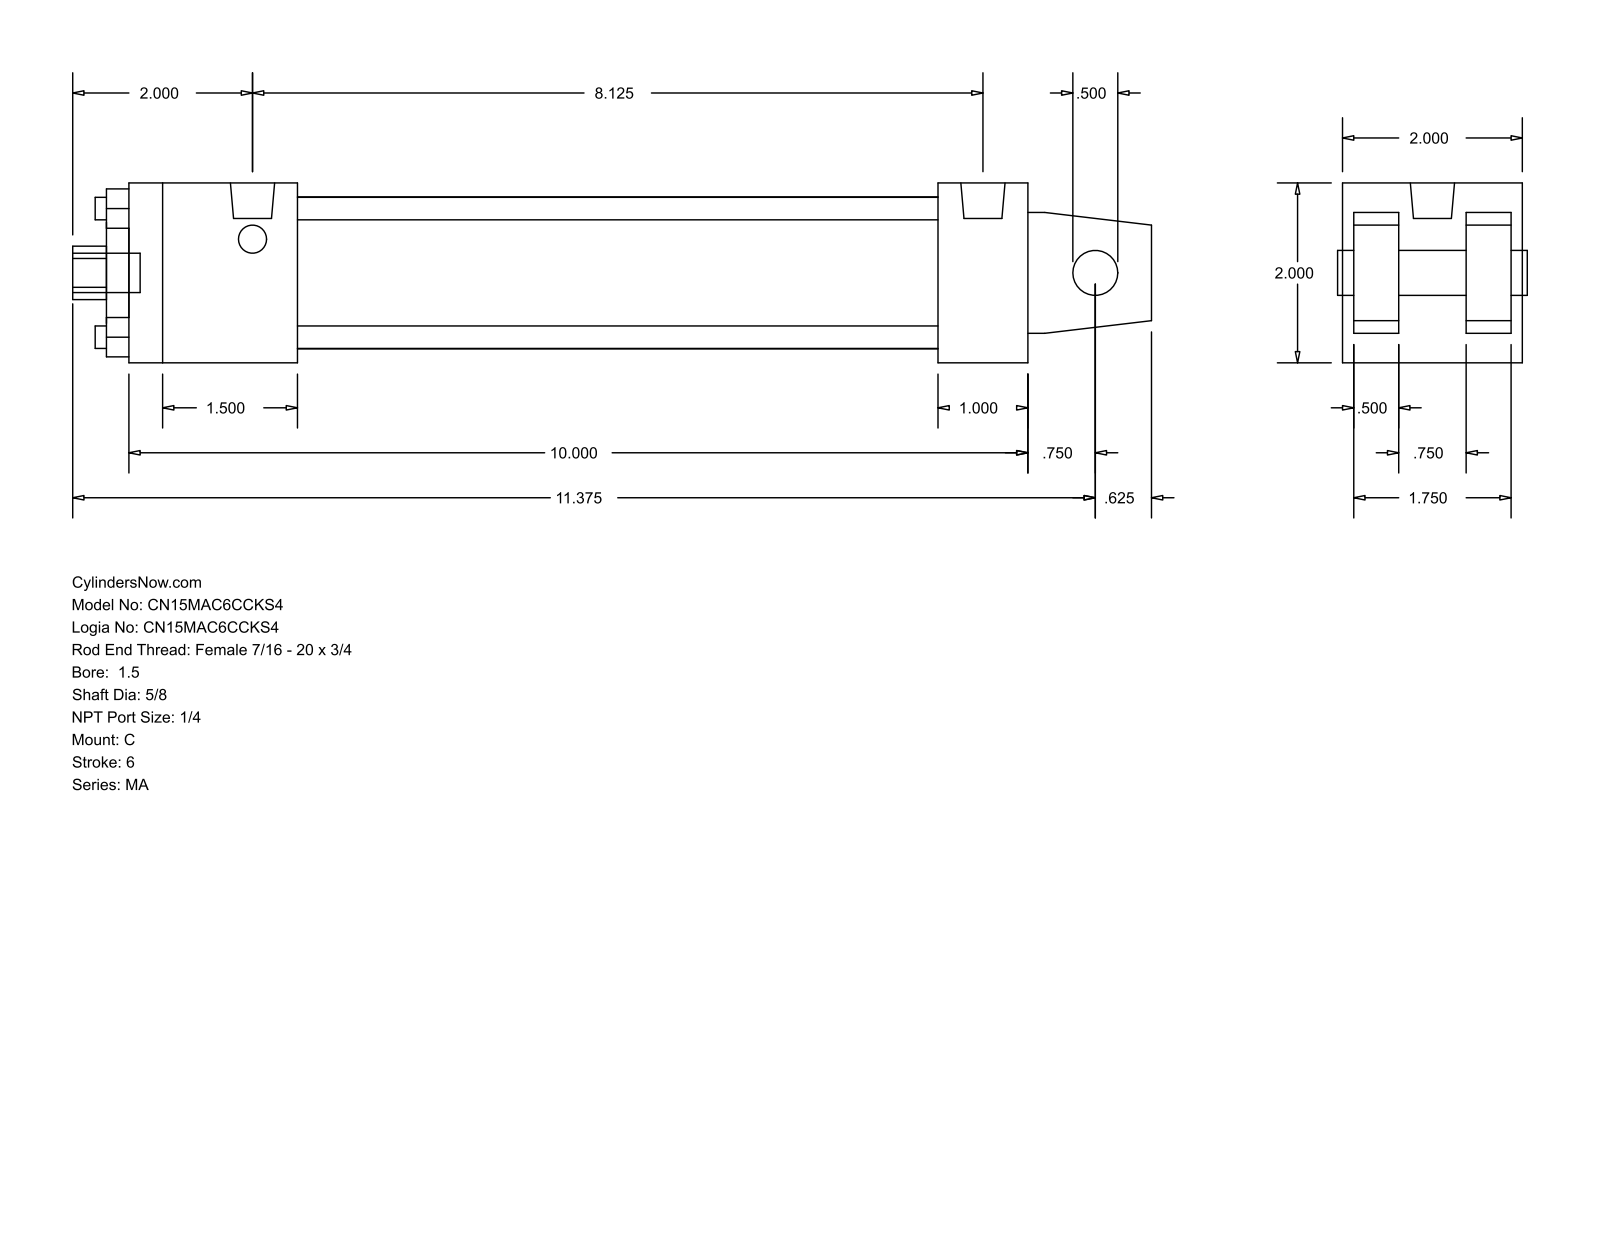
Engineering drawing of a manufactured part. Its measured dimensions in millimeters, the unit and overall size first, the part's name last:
Units: millimetres
Overall size (bounding box): 304.8 × 50.8 × 50.8
Round holes (diameter × count): ⌀6.35 ×4, ⌀12.7 ×1, ⌀15.88 ×1, ⌀28.57 ×1, ⌀42.93 ×1
Round bosses / shafts (diameter × count): ⌀7.94 ×4, ⌀12.49 ×2, ⌀11.11 ×1
Partial cylindrical surfaces — rounded edges, fillets, slot ends (radius × count): R7.54 ×1
Main face-to-face distances: 50.8, 12.7, 3.17, 15.87, 34.93, 47.63, 31.76, 254, 228.59, 25.41
Hole centre spacings: 25.68, 36.32, 51.36
Bodies: 0 solids, 103 faces (76 planar, 27 cylindrical, 0 other)
Part name (STEP PRODUCT): MA_C__0150_0.625
STEP written by: GSSL Pune (CONFIG_CONTROL_DESIGN)
